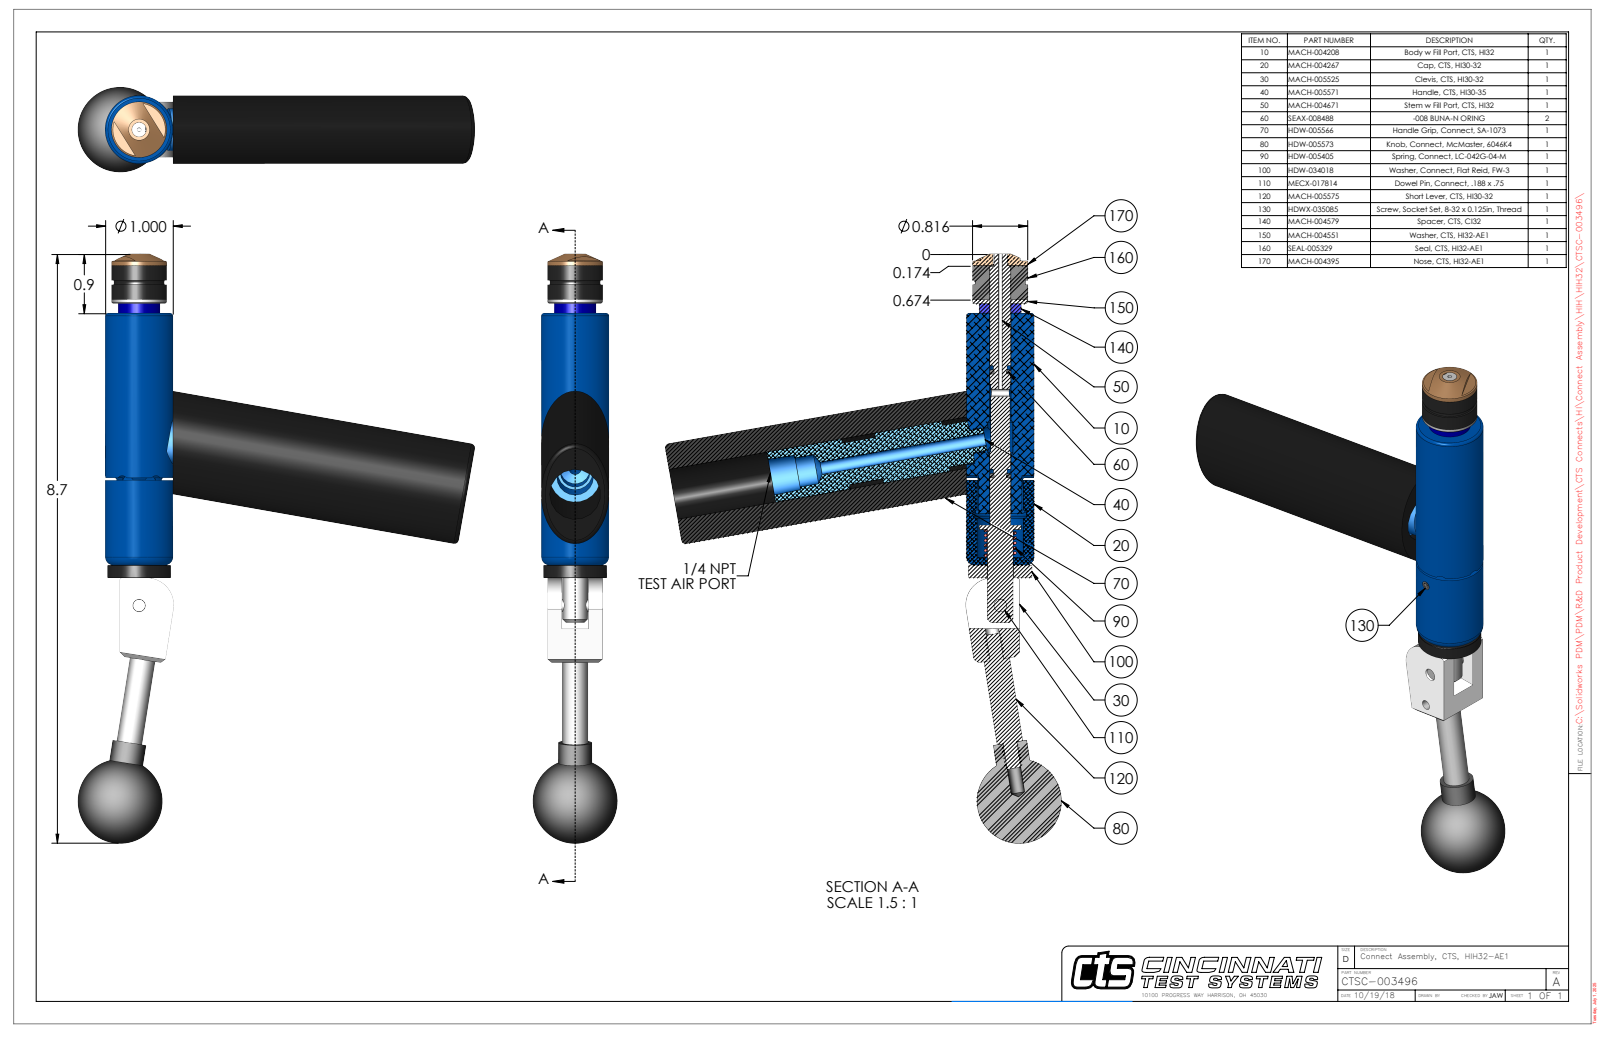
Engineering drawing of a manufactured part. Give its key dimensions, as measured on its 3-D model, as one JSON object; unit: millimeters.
{"part_name": "CTSC-003496", "step_written_by": "SolidWorks 2023 (AUTOMOTIVE_DESIGN)", "units": "millimeters", "bodies": {"solids": 11, "faces": 295, "planar": 101, "cylindrical": 126, "other": 68}, "overall_size": [221.1, 148.7, 31.8], "volume_mm3": 154700, "surface_area_mm2": 50860, "round_holes": [[5.1, 2], [1.6, 1], [2.8, 1], [3.5, 1], [3.8, 1], [4.7, 1], [4.8, 1], [5.4, 1], [7.9, 1], [8, 1], [8, 1], [9.8, 1]], "round_bosses_or_shafts": [[6.4, 2], [5.1, 2], [25.4, 1], [23.8, 1], [20.7, 1], [19.1, 1], [15.7, 1], [15.7, 1]], "partial_cylinders_radius": [[2.4, 6], [0.7, 2], [1.8, 1], [8.3, 1], [10.2, 1], [11.7, 1]], "face_to_face_distances": [5.3, 15.3, 12.7, 112.3, 99.6, 17.8, 5.1, 94.5, 20.6, 117], "hole_center_spacings": [15.2, 42.1, 57.2]}
